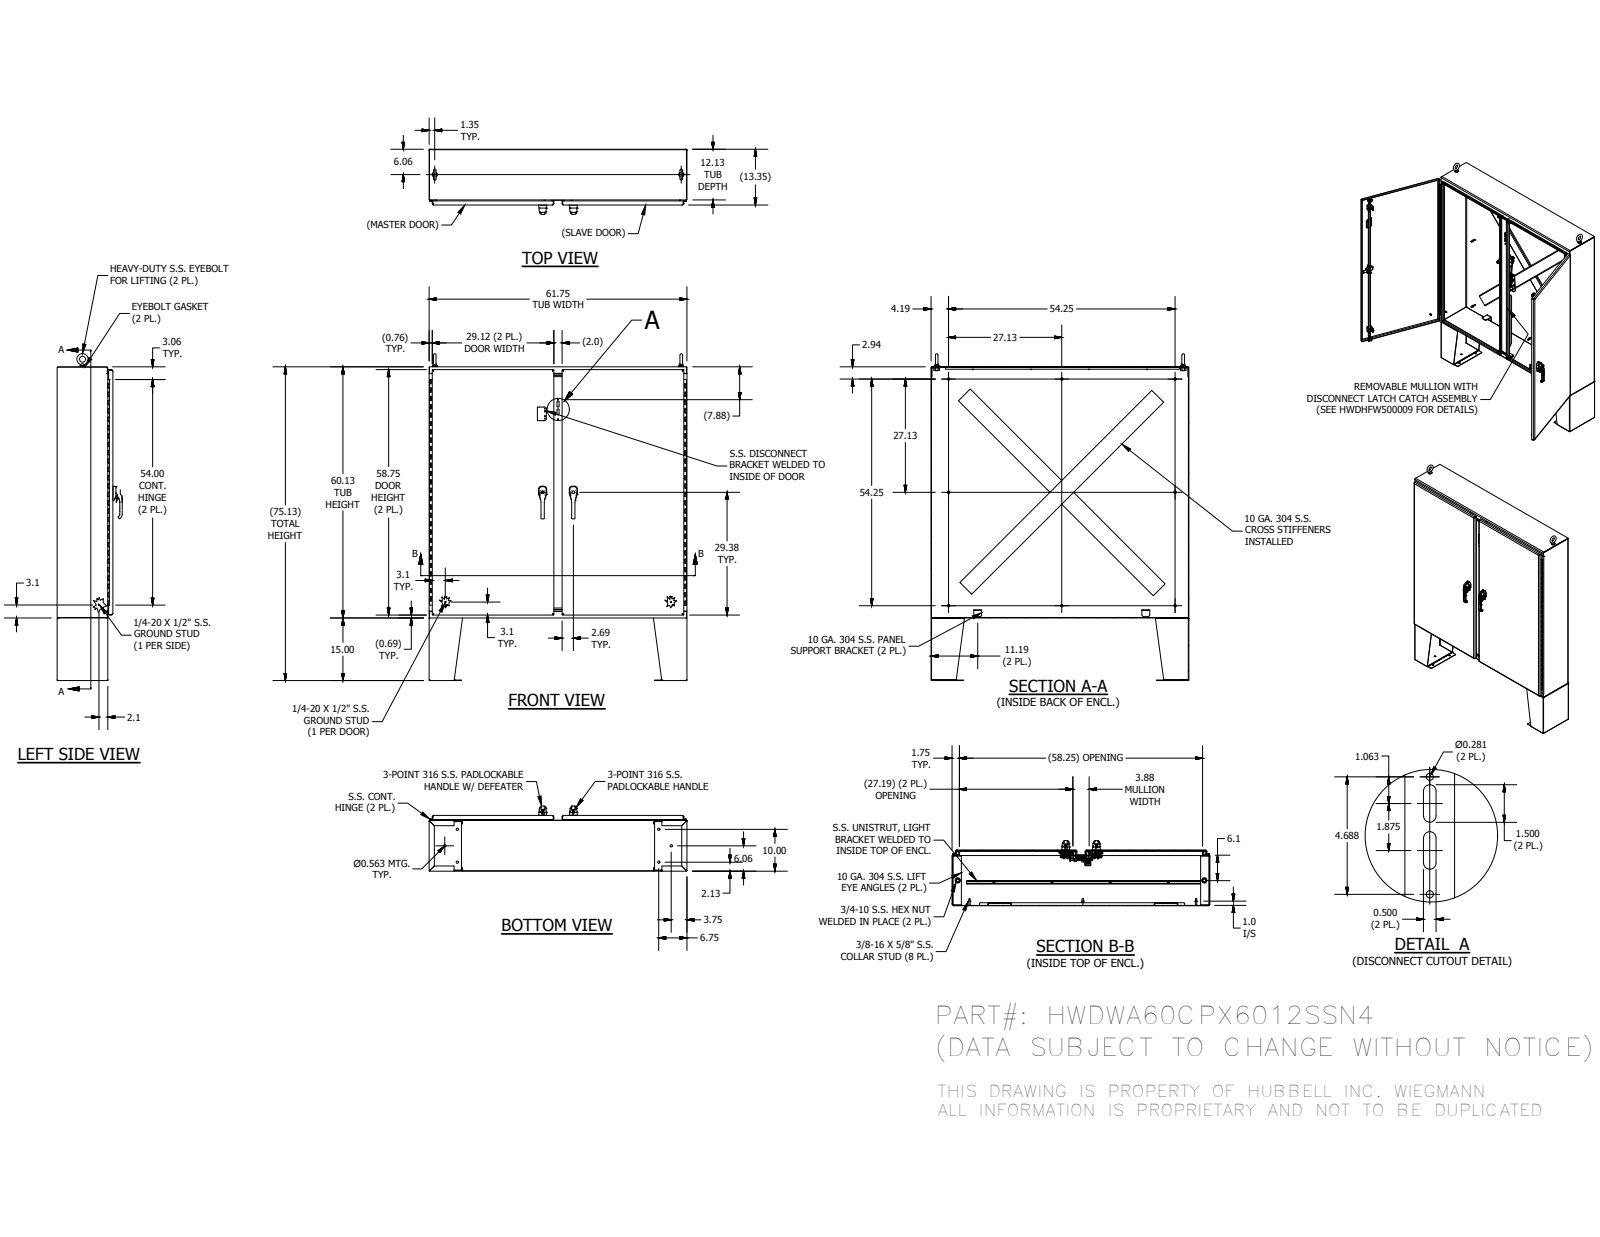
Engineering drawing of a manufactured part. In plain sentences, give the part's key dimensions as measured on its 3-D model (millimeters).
The part is named "WA60CPX6012SSN4BLR; WACPX6012SSN4TOP; WACPX6012SSN4BTM; HFW303115 (+8 more)". Its 3-D file was written by "Autodesk Inventor 2016 (AUTOMOTIVE_DESIGN)". It is 215 solids with 8808 faces: 4095 planar, 2957 cylindrical and 1756 other. Overall it measures 1987.49 by 1568.45 by 396.15 millimeters. Its volume is 24 460 000 cubic millimeters and its surface area 18 510 000 square millimeters. Round holes: 20 of diameter 6.35, 18 of diameter 9.52, 18 of diameter 14.29, 12 of diameter 4.98, 10 of diameter 7.14, 9 of diameter 4.76, 8 of diameter 6.65, 6 of diameter 3.96, 6 of diameter 4.83, 6 of diameter 5.4, 6 of diameter 7.33, 6 of diameter 7.37. Round bosses or shafts: 16 of diameter 8.38, 16 of diameter 6.35, 14 of diameter 15.88, 9 of diameter 14.29, 9 of diameter 9.52, 9 of diameter 8.56, 6 of diameter 25.4, 6 of diameter 12.7. Partial cylindrical surfaces (rounded edges, fillets, slot ends): 358 of radius 0.5, 222 of radius 0.3, 144 of radius 0.51, 58 of radius 3.17, 42 of radius 0.47, 28 of radius 1.27, 28 of radius 2, 24 of radius 3.57. The main face-to-face distances are 2.64, 336.39, 333.75, 339.03, 1524.54, 1565.8, 2.65, 3.17, 305.33, 31.06. The hole center spacings are 9.65, 19.31, 22.5, 30.36, 31.38, 37.06, 88.97, 98.31.
